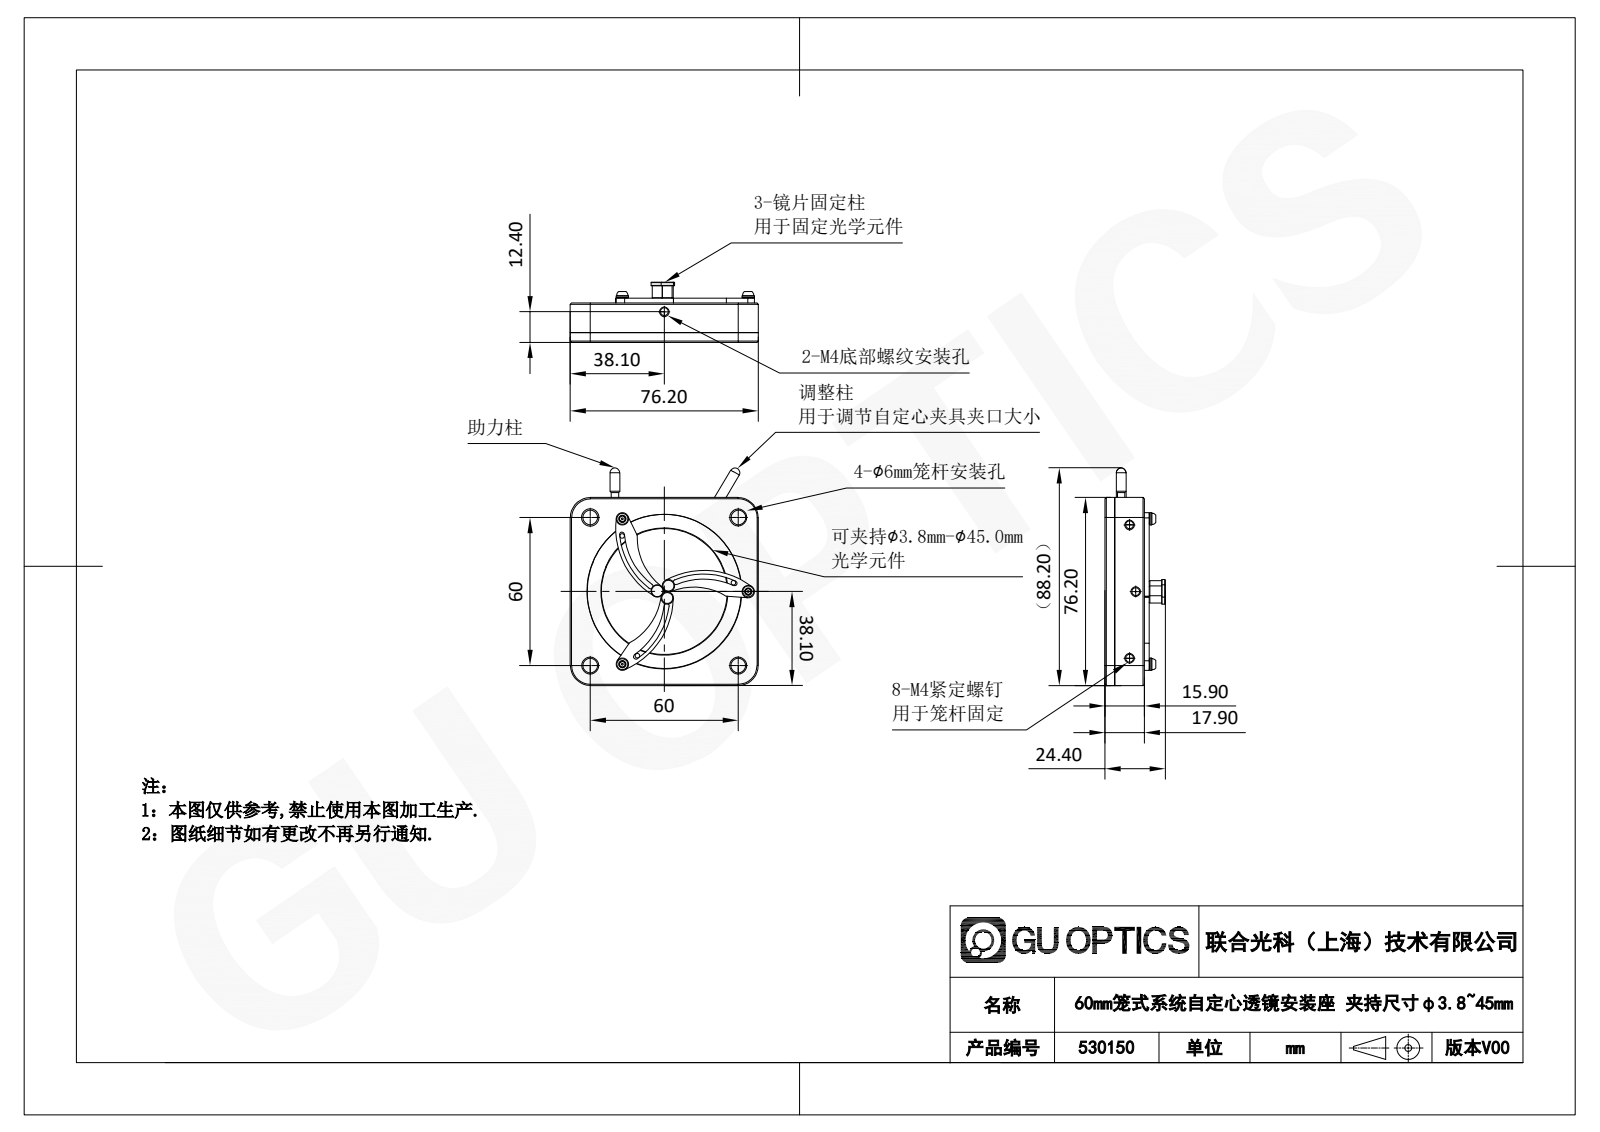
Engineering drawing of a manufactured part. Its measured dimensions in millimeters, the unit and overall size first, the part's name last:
Units: millimetres
Overall size (bounding box): 88.22 × 76.2 × 24.4
Round holes (diameter × count): ⌀5 ×5, ⌀3.3 ×4, ⌀6 ×4, ⌀2 ×3, ⌀62.7 ×1
Round bosses / shafts (diameter × count): ⌀4 ×5, ⌀6.5 ×4, ⌀6 ×4, ⌀3.4 ×3, ⌀62.5 ×1, ⌀51 ×1, ⌀5 ×1, ⌀3 ×1
Partial cylindrical surfaces — rounded edges, fillets, slot ends (radius × count): R1 ×6, R8.1 ×4, R25 ×3, R28.5 ×3, R30.5 ×3, R32 ×3
Main face-to-face distances: 3.9, 15.9, 12, 8.9, 5, 7, 76.2, 6.7, 15.6, 11.7
Hole centre spacings: 42.43, 60, 2.89, 48.93, 5, 6.95, 26.39, 27.51
Bodies: 0 solids, 247 faces (105 planar, 72 cylindrical, 70 other)
Part name (STEP PRODUCT): 530150
STEP written by: SolidWorks 2020 (CONFIG_CONTROL_DESIGN)
